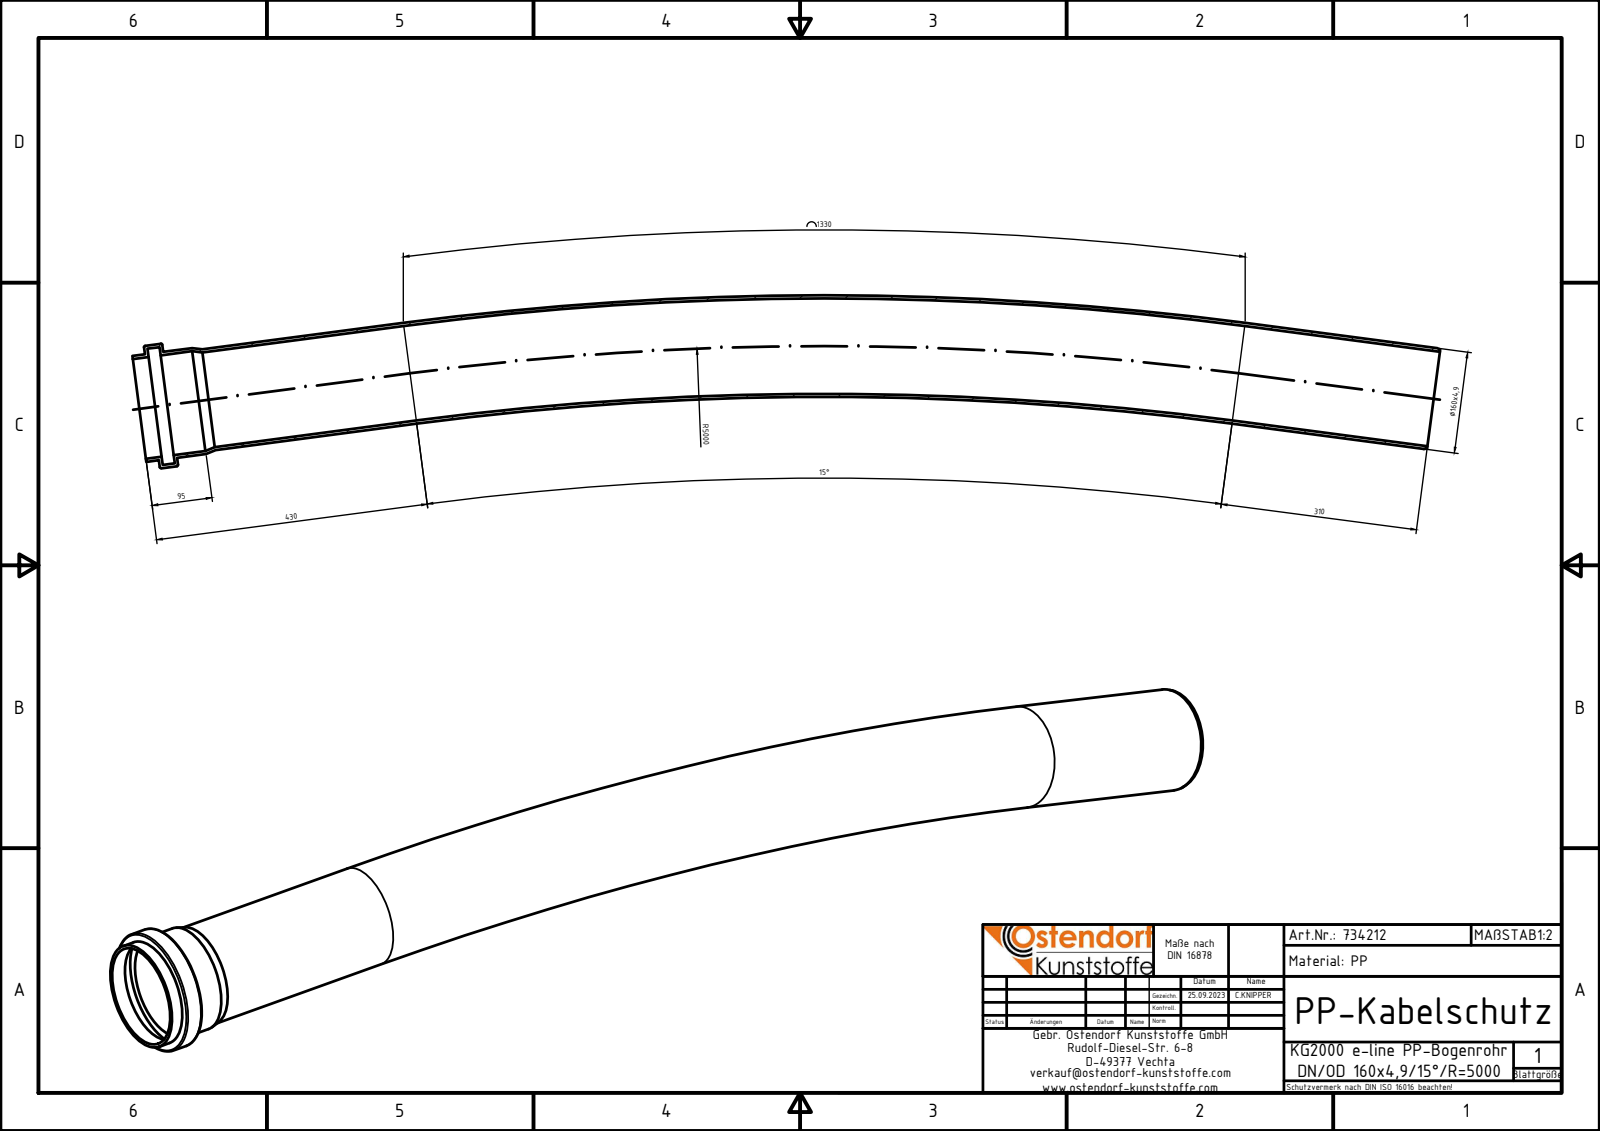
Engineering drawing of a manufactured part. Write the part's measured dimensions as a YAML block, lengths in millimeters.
part_name: "734212z"
step_written_by: "Autodesk Inventor 2024 (AUTOMOTIVE_DESIGN)"
units: millimeters
bodies: {solids: 3, faces: 27, planar: 10, cylindrical: 10, other: 7}
overall_size: [1550.97, 256.01, 194.5]
volume: 3766000
surface_area: 1551000
round_holes:
  - {diameter: 150.2, count: 2}
  - {diameter: 158.5, count: 2}
  - {diameter: 184.7, count: 1}
round_bosses_or_shafts:
  - {diameter: 168.3, count: 2}
  - {diameter: 160, count: 2}
  - {diameter: 194.5, count: 1}
face_to_face_distances: [4.89, 24.09, 19.2, 28.98, 20, 24.89, 44.09, 48.98, 434.84, 414.84]
